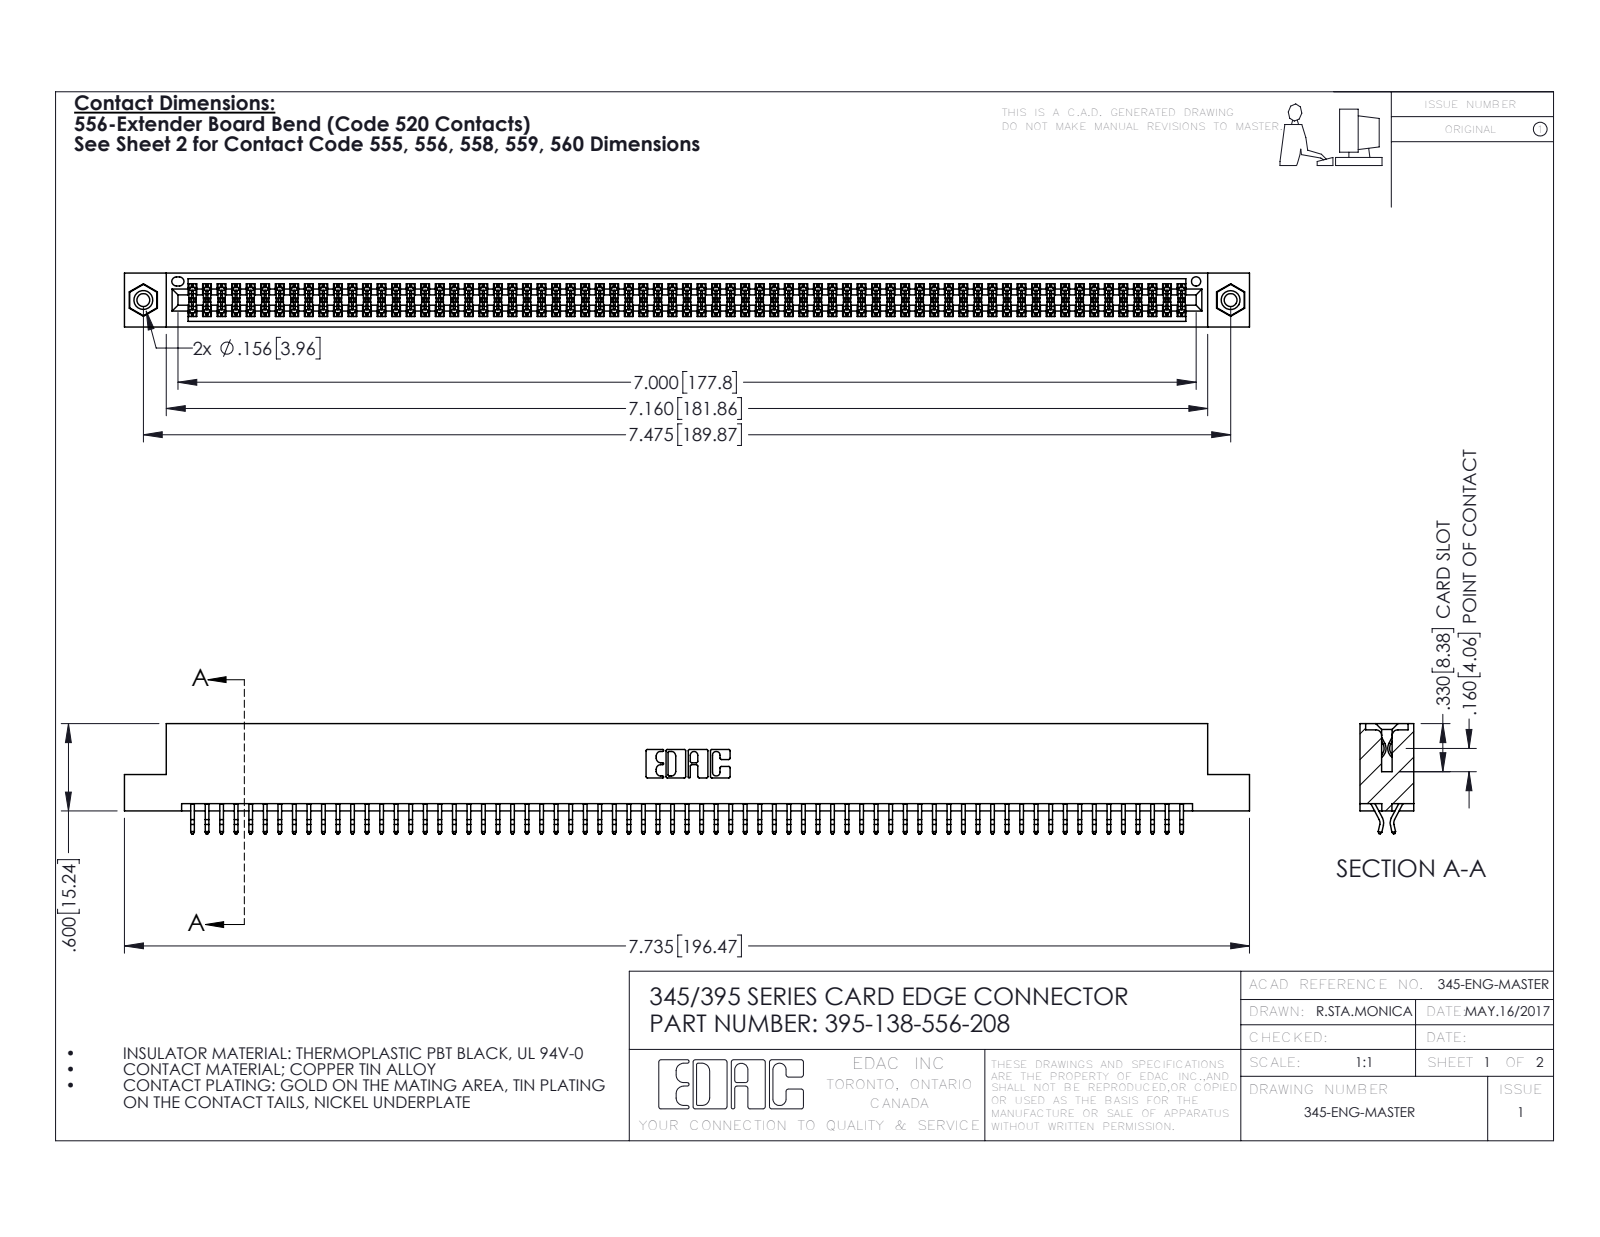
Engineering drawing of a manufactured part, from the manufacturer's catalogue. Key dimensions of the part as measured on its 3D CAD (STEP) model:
Part name (STEP PRODUCT): 345 Part_Flush Mounting Lugs - 0.156 Dia-TI; 345-250-001_345-250-003-102; 395-138-556-208; 345-292-001_556 Tail
STEP written by: SolidWorks 2016 (CONFIG_CONTROL_DESIGN)
Units: inches
Bodies: 141 solids, 7914 faces (5218 planar, 2680 cylindrical, 16 other)
Overall size (bounding box): 7.735 × 0.757 × 0.37
Volume: 1.179 in³ · Surface area: 44.92 in²
Round holes (diameter × count): ⌀0.089 ×2, ⌀0.125 ×2, ⌀0.156 ×2, ⌀0.064 ×1
Round bosses / shafts (diameter × count): ⌀0.155 ×2
Partial cylindrical surfaces — rounded edges, fillets, slot ends (radius × count): R0.006 ×207, R0.01 ×22, R0.007 ×6, R0.031 ×6, R0.026 ×3, R0.01 ×2, R0.014 ×2, R0.019 ×2
Main face-to-face distances: 0.072, 0.298, 0.37, 0.2, 0.025, 0.098, 0.272, 0.225, 0.175, 0.149
Hole centre spacings: 0.27, 7.239, 7.475
